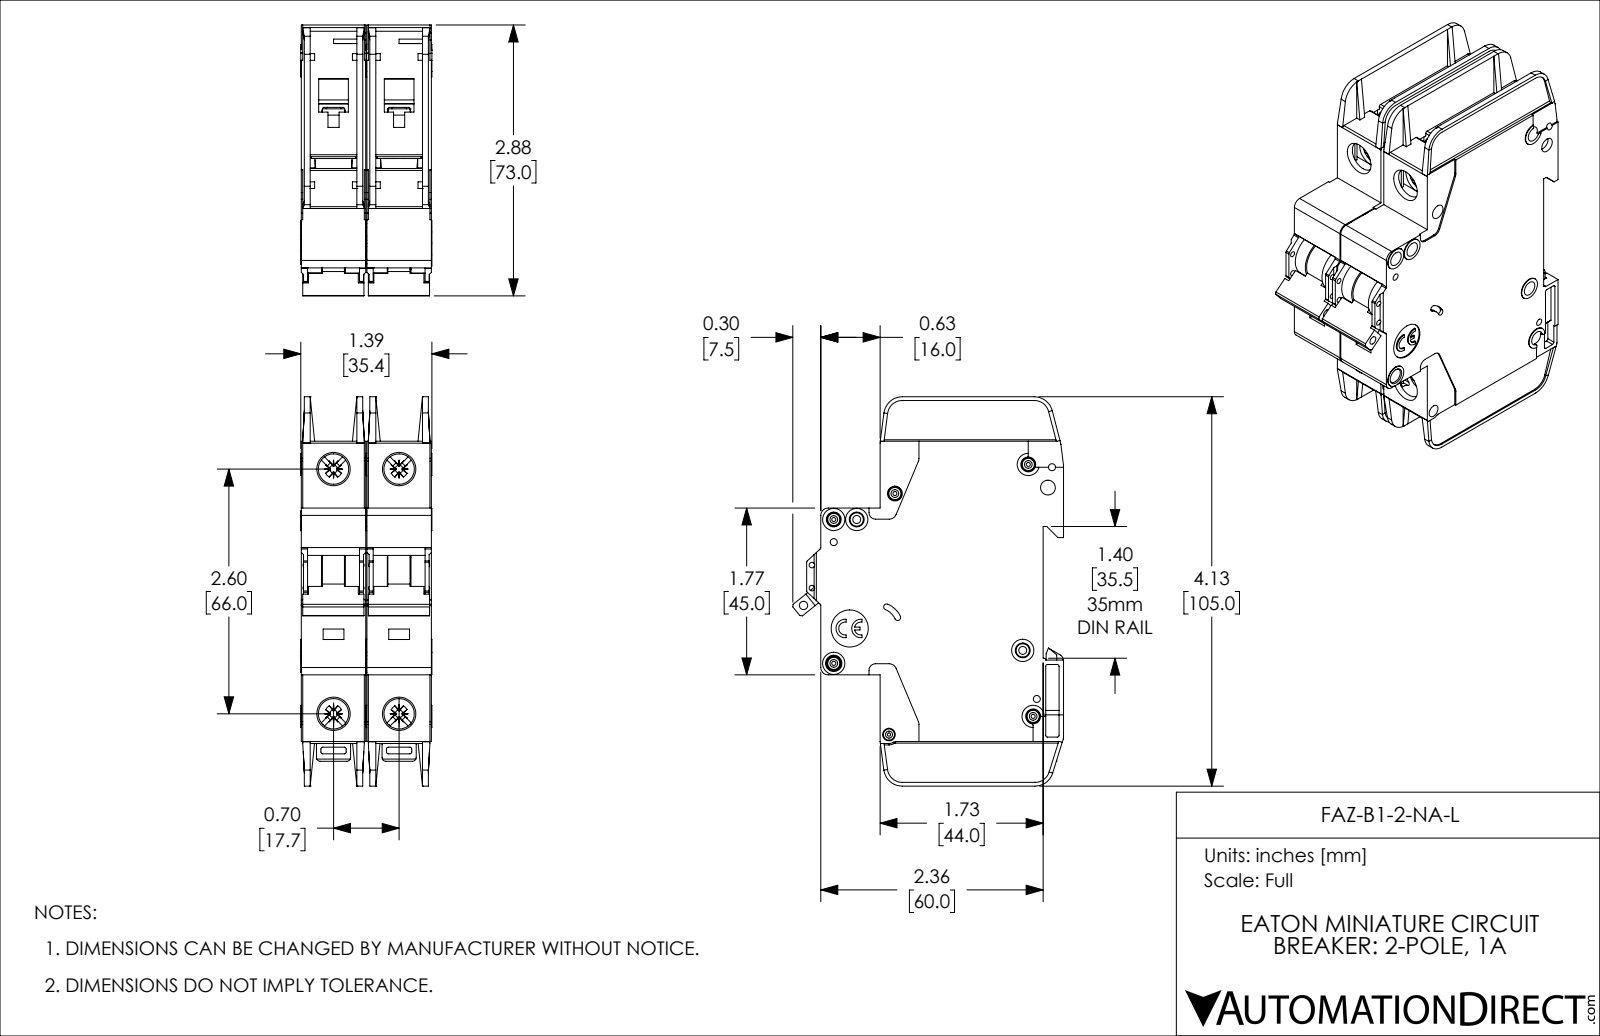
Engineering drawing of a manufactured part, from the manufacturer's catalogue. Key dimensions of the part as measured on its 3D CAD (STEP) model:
Part name (STEP PRODUCT): FAZ-B1-2-NA-L
STEP written by: SolidWorks 2019 (AUTOMOTIVE_DESIGN)
Units: inches
Bodies: 2 solids, 2254 faces (1342 planar, 714 cylindrical, 198 other)
Overall size (bounding box): 4.134 × 2.876 × 1.394
Volume: 9.365 in³ · Surface area: 82.01 in²
Round holes (diameter × count): ⌀0.157 ×8, ⌀0.043 ×5, ⌀0.075 ×4, ⌀0.323 ×4, ⌀0.059 ×2, ⌀0.085 ×2, ⌀0.035 ×1, ⌀0.089 ×1, ⌀0.098 ×1, ⌀0.134 ×1, ⌀0.394 ×1
Round bosses / shafts (diameter × count): ⌀0.13 ×5, ⌀0.236 ×4, ⌀0.118 ×3, ⌀0.098 ×2
Partial cylindrical surfaces — rounded edges, fillets, slot ends (radius × count): R0.02 ×57, R0.016 ×20, R0.039 ×14, R0.079 ×10, R0.043 ×8, R0.008 ×5, R0.197 ×5, R0.01 ×4
Main face-to-face distances: 0.697, 0.047, 0.685, 0.591, 0.094, 0.638, 0.543, 1.382, 0.744, 0.65
Hole centre spacings: 0.244, 0.537, 0.697, 0.87, 2.598, 2.69, 0.189, 0.199
